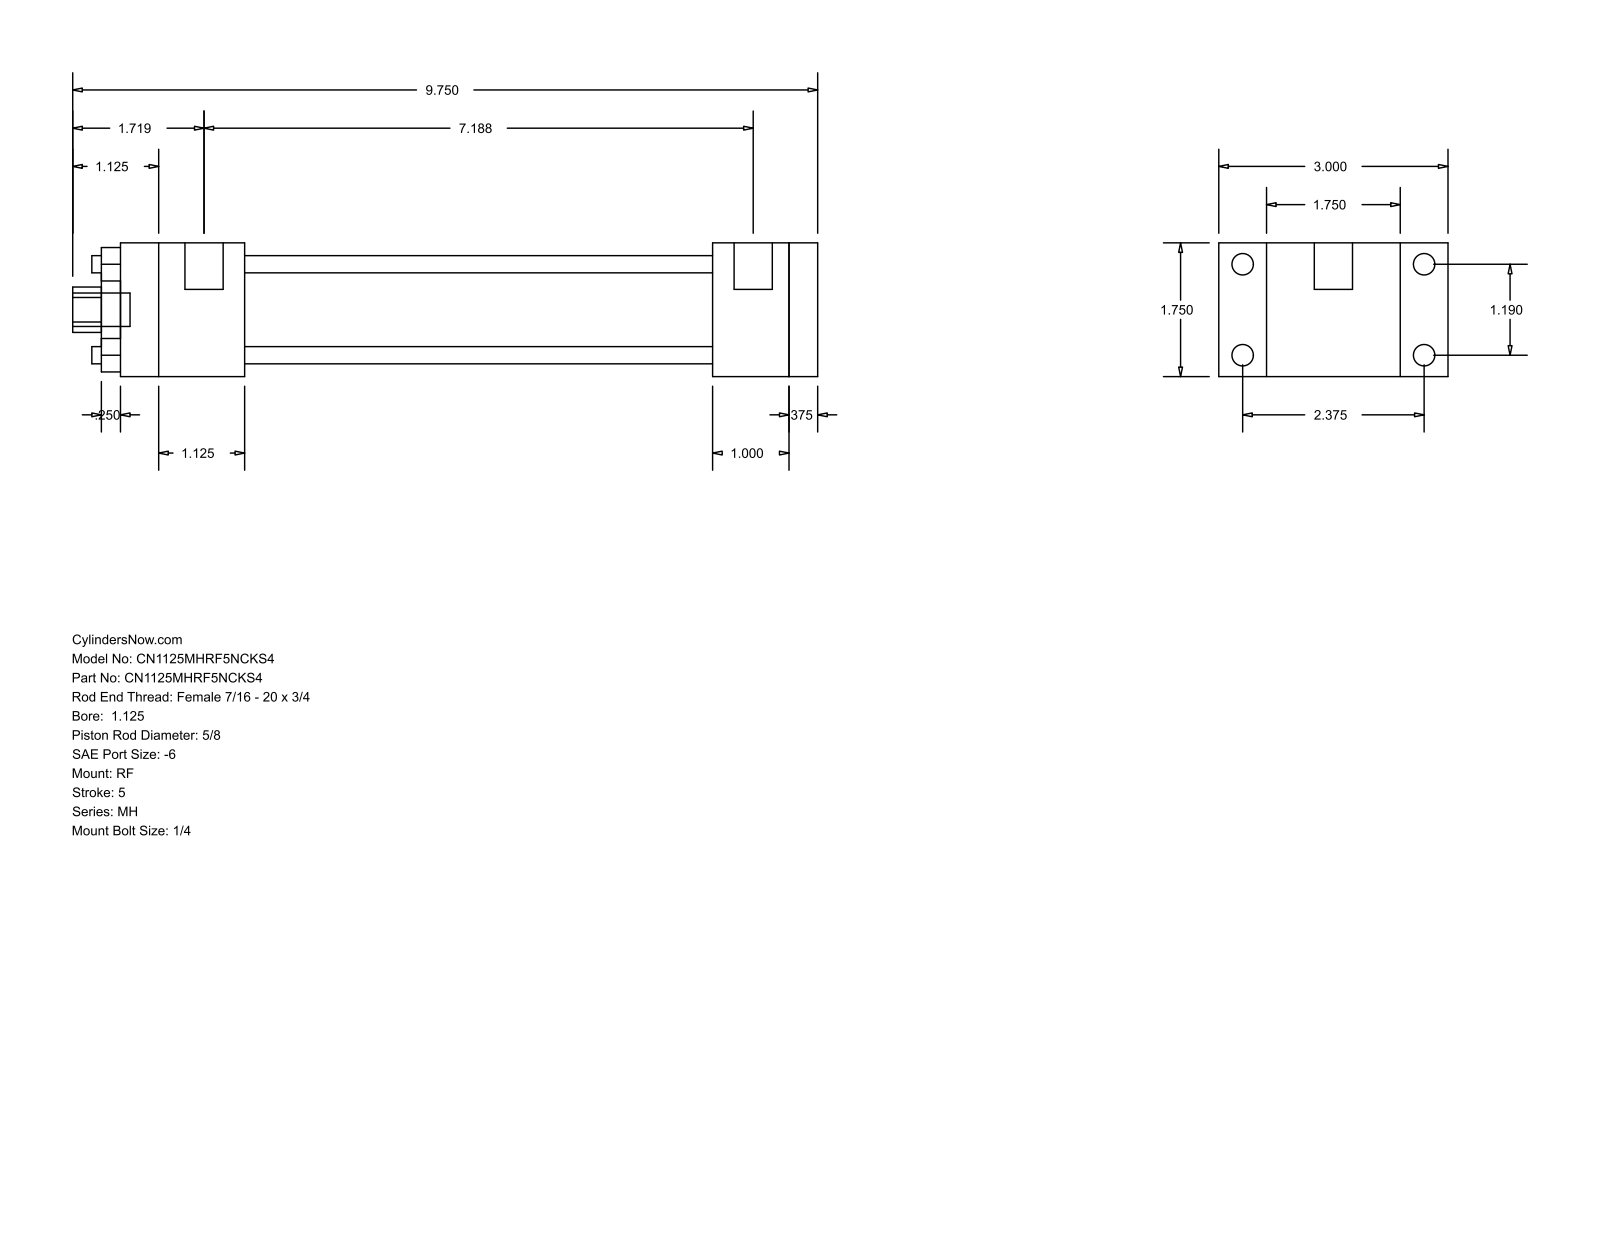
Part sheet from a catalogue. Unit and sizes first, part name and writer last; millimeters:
Units: millimetres
Overall size (bounding box): 247.65 × 76.2 × 44.45
Round holes (diameter × count): ⌀5.71 ×4, ⌀15.88 ×1, ⌀28.57 ×1, ⌀34.92 ×1
Round bosses / shafts (diameter × count): ⌀7.14 ×4, ⌀5.56 ×4, ⌀12.7 ×2, ⌀11.11 ×1
Partial cylindrical surfaces — rounded edges, fillets, slot ends (radius × count): R7.54 ×1
Main face-to-face distances: 44.46, 9.53, 231.77, 15.87, 180.97, 190.5, 155.57, 25.4, 34.93, 41.27
Hole centre spacings: 21.37, 30.22, 42.74
Bodies: 0 solids, 92 faces (64 planar, 28 cylindrical, 0 other)
Part name (STEP PRODUCT): MH_RF__0112_0.625
STEP written by: GSSL Pune (CONFIG_CONTROL_DESIGN)
